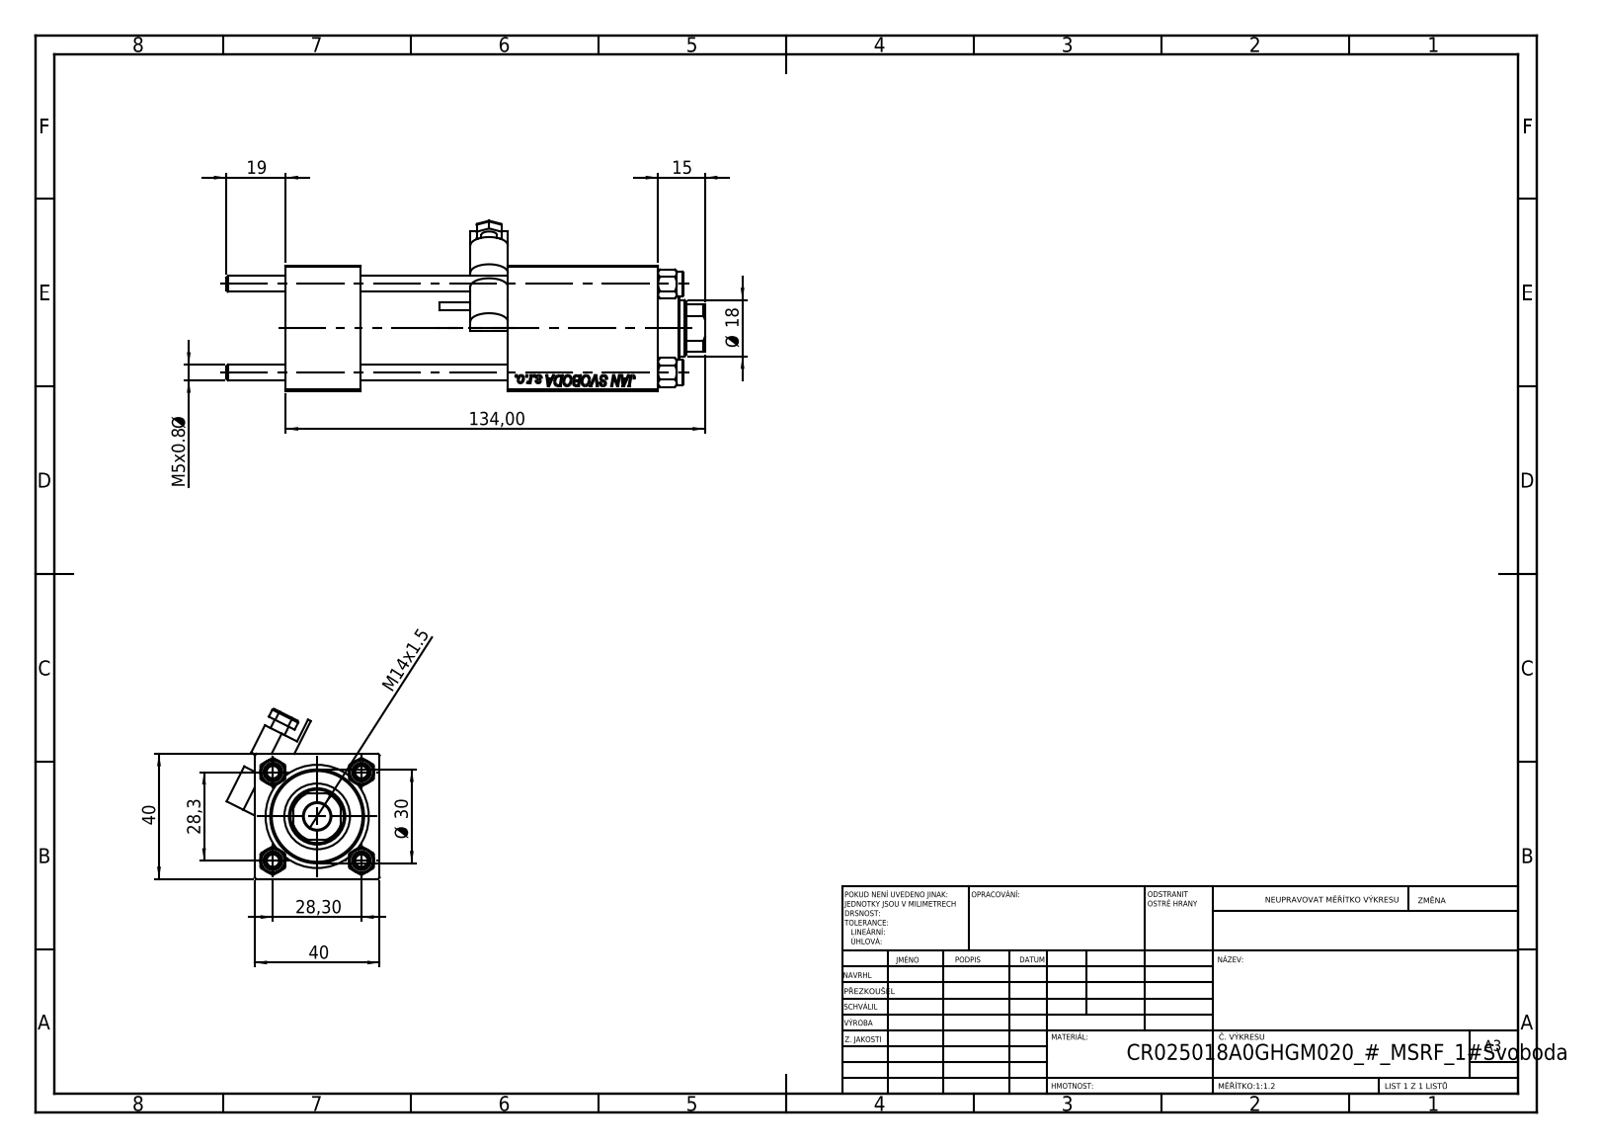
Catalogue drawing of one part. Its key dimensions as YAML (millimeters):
part_name: "NUT_M5; V215_VC_A; V215CR_BODY_A; CR025_012_A_0_G_A_G_M_020_+#_##_TYCINKA (+2 more)"
step_written_by: "SolidWorks 2019 (CONFIG_CONTROL_DESIGN)"
units: millimeters
bodies: {solids: 12, faces: 1160, planar: 534, cylindrical: 90, other: 536}
overall_size: [153, 54.35, 48.93]
volume: 155882
surface_area: 63222
round_holes:
  - {diameter: 5, count: 4}
  - {diameter: 20, count: 3}
  - {diameter: 7, count: 2}
  - {diameter: 13.16, count: 2}
  - {diameter: 8.5, count: 1}
  - {diameter: 18, count: 1}
  - {diameter: 21, count: 1}
  - {diameter: 25, count: 1}
  - {diameter: 30, count: 1}
round_bosses_or_shafts:
  - {diameter: 8, count: 4}
  - {diameter: 31, count: 1}
  - {diameter: 5, count: 1}
  - {diameter: 2.5, count: 1}
partial_cylinders:
  - {radius: 0.5, count: 6}
  - {radius: 6, count: 2}
  - {radius: 8.5, count: 1}
face_to_face_distances: [40, 24, 71, 47, 90.3, 66.3, 19.3, 8, 119, 95]
hole_center_spacings: [20.01, 28.3, 40.02, 72]
